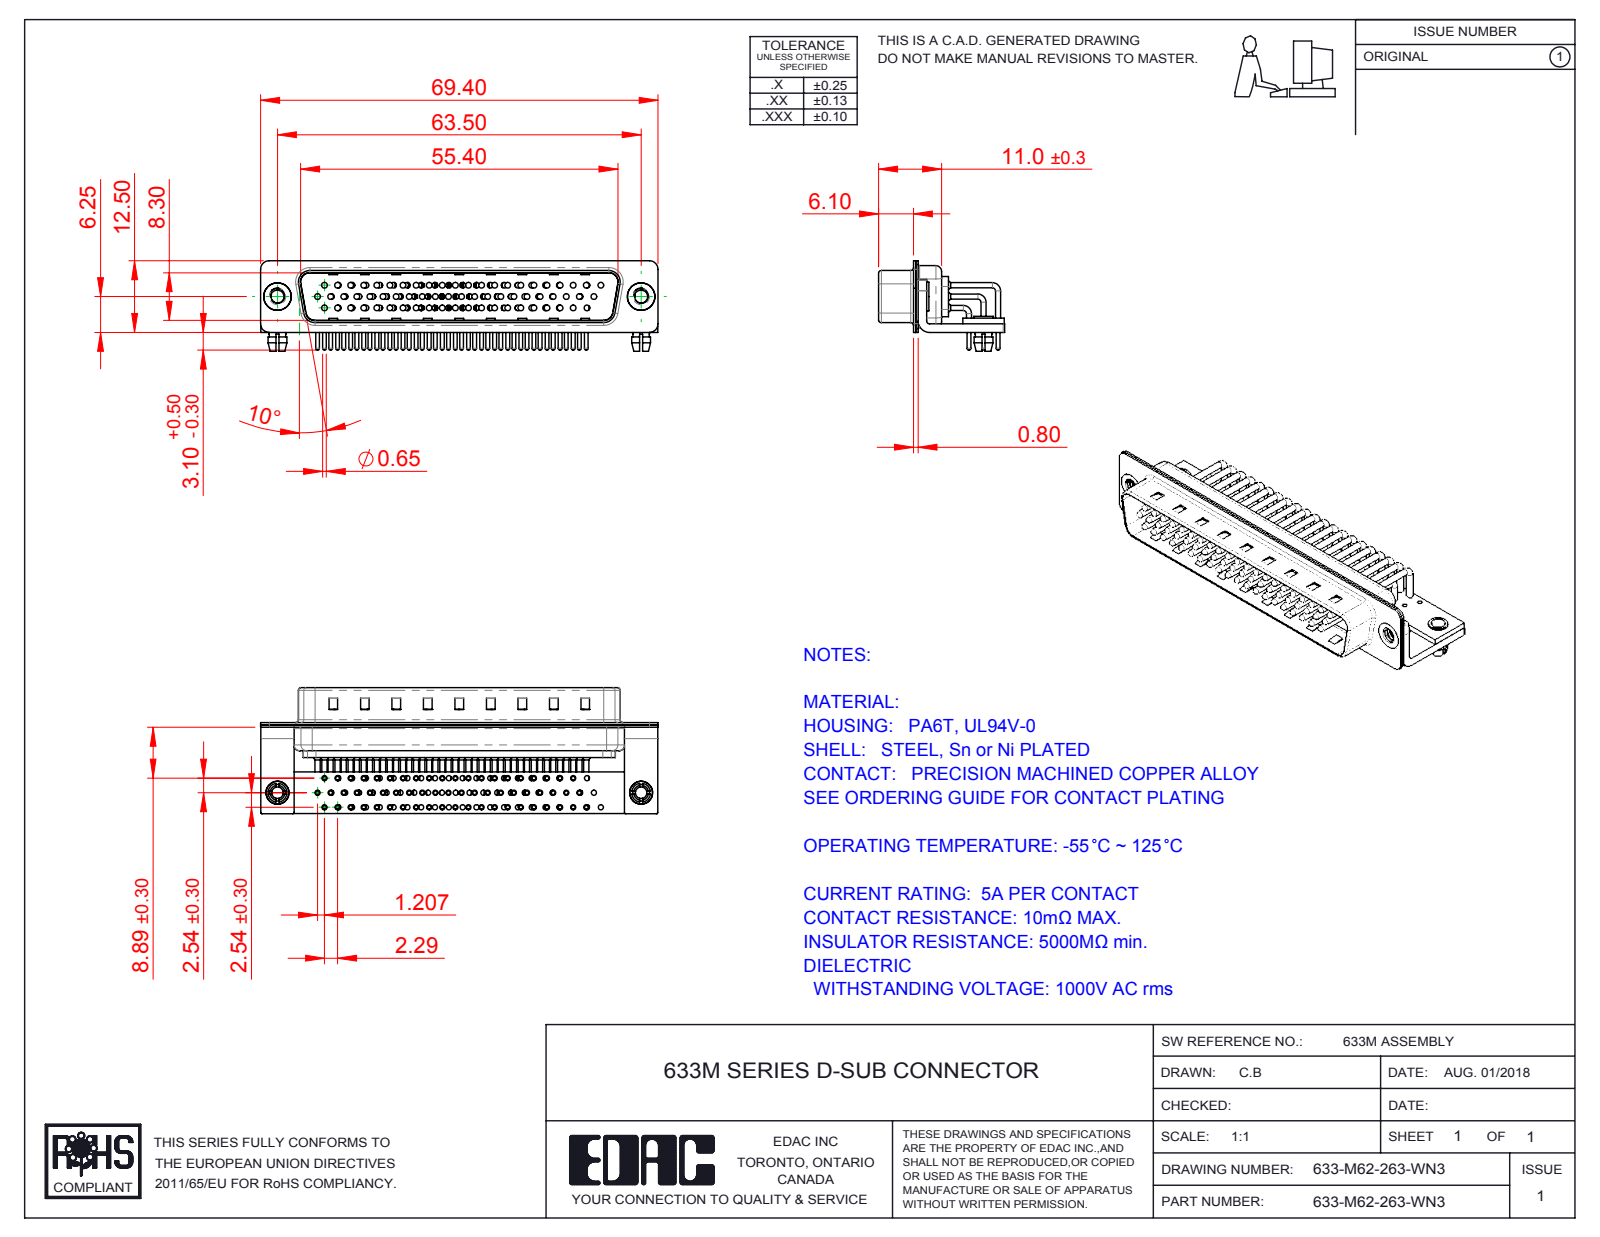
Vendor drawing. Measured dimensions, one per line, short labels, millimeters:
name: 633M Contact Row 2; 633M Stabilizer Bracket; 633M Contact Row 3; 633M Stabilizer Board_62 Contacts (+7 more)
written by: SolidWorks 2016 (CONFIG_CONTROL_DESIGN)
unit: mm
bodies: 72 solids, 7498 faces (4245 planar, 2551 cylindrical, 702 other)
size: 69.4 × 22 × 15.8
volume: 5 119 mm³; area: 15 736 mm²
holes: 64× ⌀2, 62× ⌀0.9, 62× ⌀1, 62× ⌀1.7, 2× ⌀2.26, 2× ⌀2.5, 2× ⌀3.2, 2× ⌀4, 2× ⌀4.8
bosses: 118× ⌀0.9, 62× ⌀1.5, 62× ⌀0.65, 56× ⌀1, 2× ⌀5, 2× ⌀4.9, 2× ⌀4, 2× ⌀3.4
rounds: 62× R1.01, 16× R0.25, 16× R1.5, 13× R2, 9× R0.5, 8× R1.6, 4× R0.6, 4× R0.65
face distances: 0.4, 0.85, 1.25, 1.5, 9.55, 1, 1.9, 10.4, 0.8, 8.3
hole spacings: 7.24, 2.41, 9.65, 4.83, 14.48, 16.89, 2.81, 2.32
